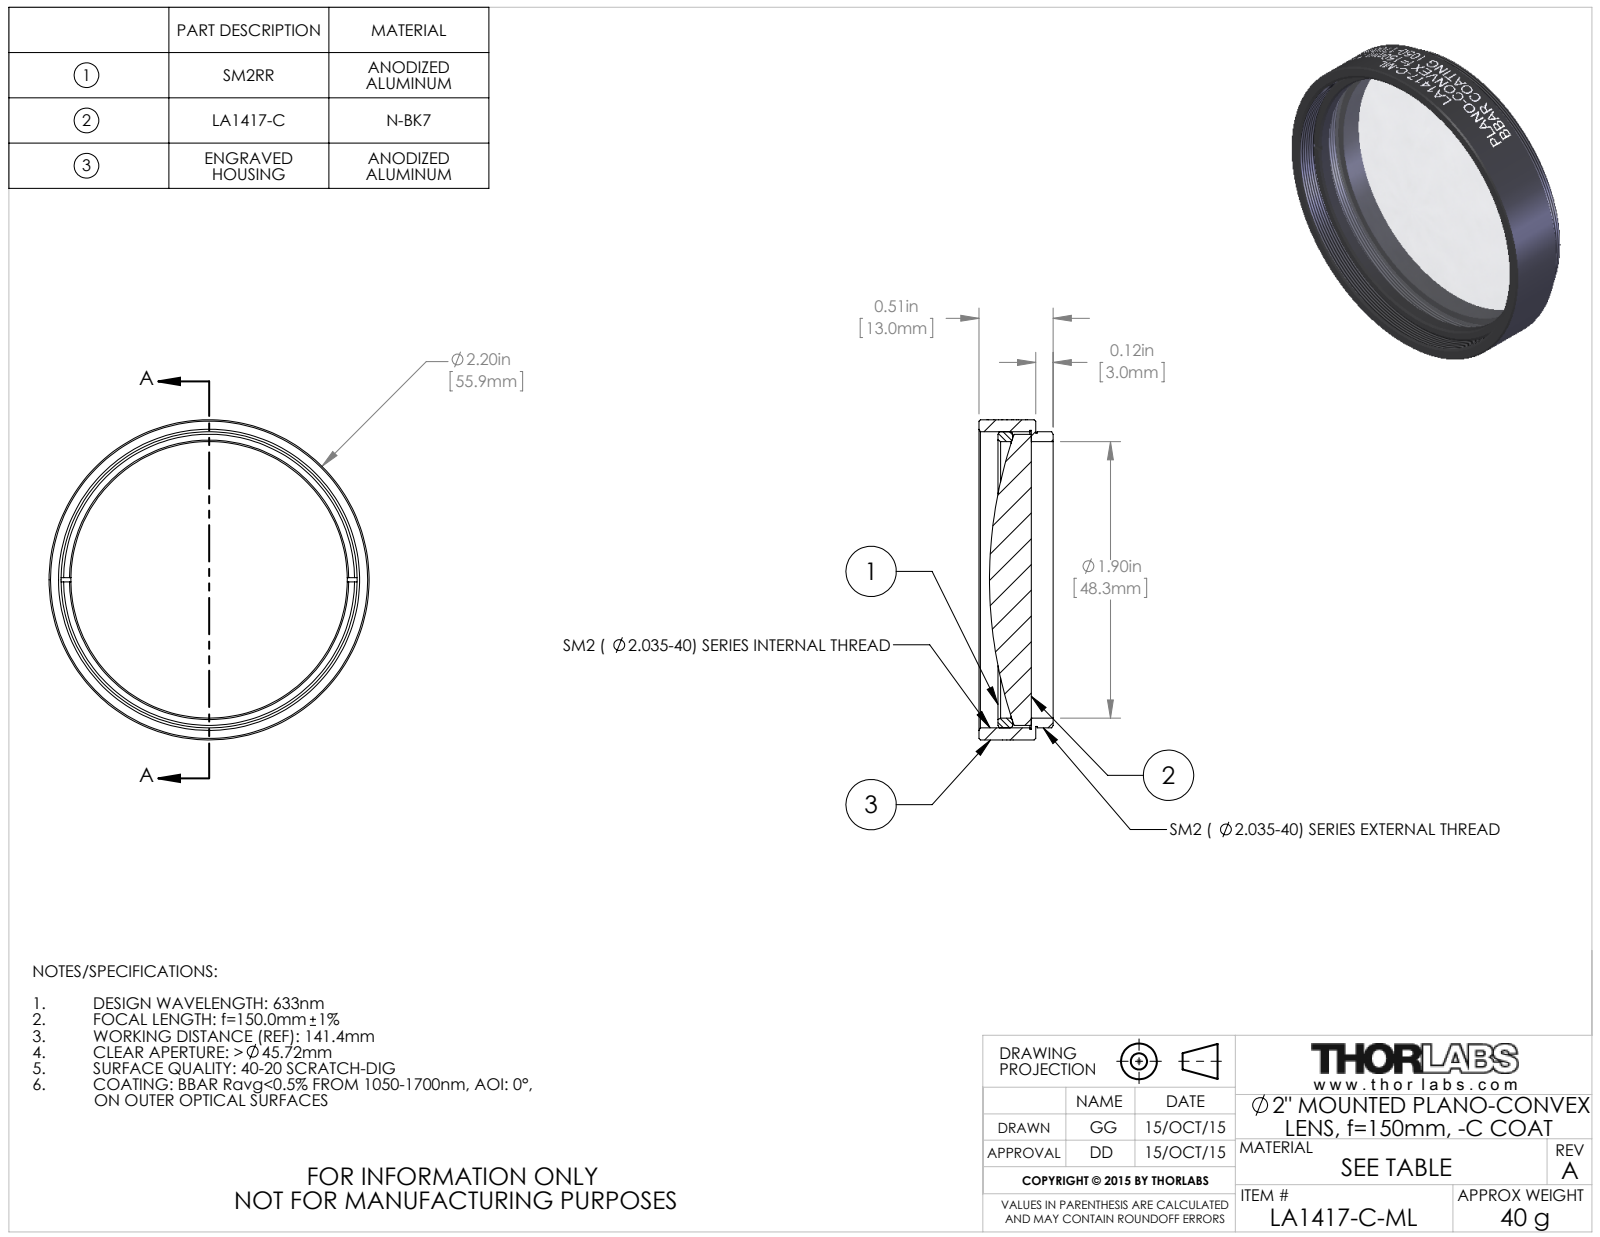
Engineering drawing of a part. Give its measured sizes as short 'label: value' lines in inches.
name: TTN039591-E0W
written by: SolidWorks 2014 (CONFIG_CONTROL_DESIGN)
unit: in
bodies: 3 solids, 147 faces (16 planar, 107 cylindrical, 24 other)
size: 2.2 × 2.2 × 0.51
volume: 0.952 in³; area: 17.66 in²
holes: 1× ⌀1.9, 1× ⌀2.055
bosses: 1× ⌀2.2, 1× ⌀2.035, 1× ⌀2.015, 1× ⌀2
face distances: 0.03, 0.39, 0.36, 0.12, 0.15, 0.51, 0.279, 0.159, 0.129, 0.231
